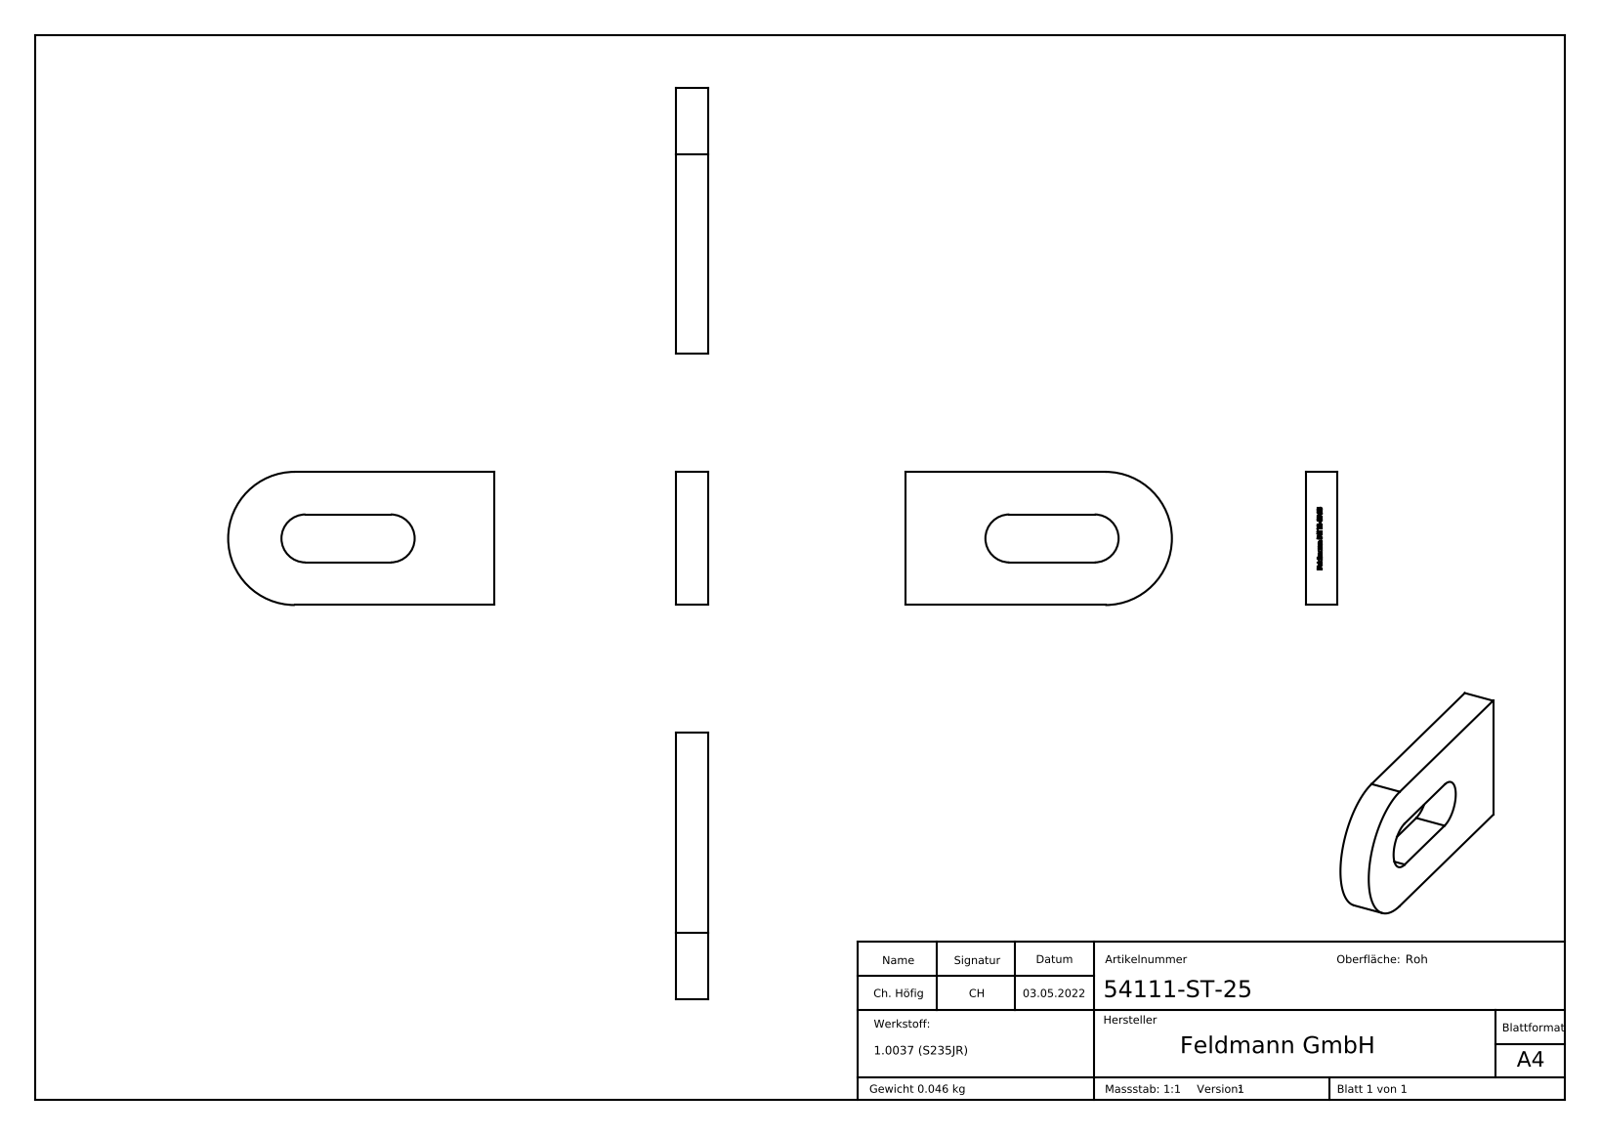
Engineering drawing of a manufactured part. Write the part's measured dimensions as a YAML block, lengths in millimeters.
part_name: "54111-ST-25"
step_written_by: "SolidWorks 2018 (CONFIG_CONTROL_DESIGN)"
units: millimeters
bodies: {solids: 1, faces: 239, planar: 151, cylindrical: 3, other: 85}
overall_size: [50, 25, 6]
volume: 5852
surface_area: 3153
partial_cylinders:
  - {radius: 4.5, count: 2}
  - {radius: 12.5, count: 1}
face_to_face_distances: [6, 25, 8, 17, 9, 0.61, 3, 0.79, 2.65, 8.48]
